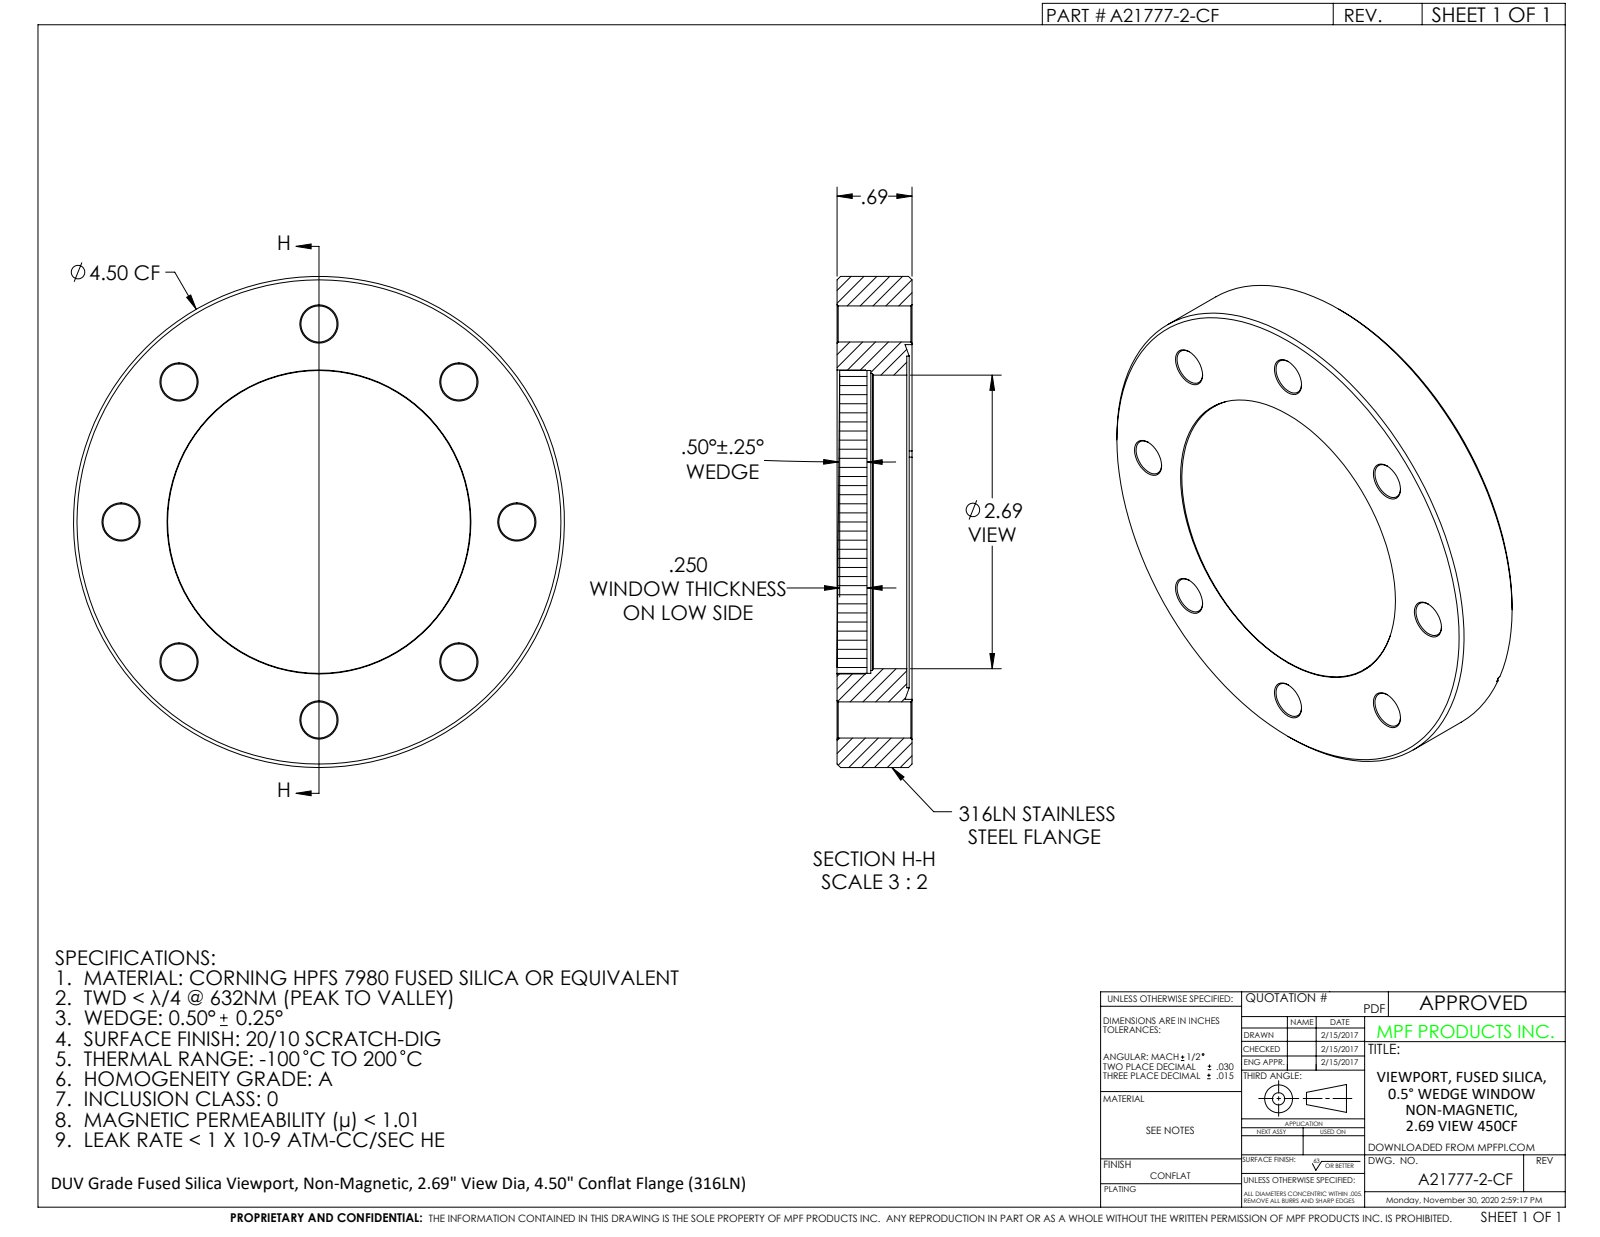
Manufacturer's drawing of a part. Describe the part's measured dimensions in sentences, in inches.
The part is named "A21777-1-CF". Its 3-D file was written by "SolidWorks 2020 (CONFIG_CONTROL_DESIGN)". It is 2 solids with 87 faces: 14 planar, 32 cylindrical and 41 other. Overall it measures 4.5 by 4.5 by 0.688 inches. Its volume is 7.879 cubic inches and its surface area 54.72 square inches. Round holes: 8 of diameter 0.331, 1 of diameter 2.69, 1 of diameter 2.72, 1 of diameter 2.775, 1 of diameter 3.04, 1 of diameter 3.25. Round bosses or shafts: 1 of diameter 4.5. Partial cylindrical surfaces (rounded edges, fillets, slot ends): 1 of radius 1.433, 1 of radius 1.453. The main face-to-face distances are 0.687, 0.274, 0.413, 0.639, 0.365, 0.048, 0.309, 0.035, 0.33, 0.378. The hole center spacings are 1.389, 1.814, 3.352, 2.565, 2.566, 3.628, 3.628.
